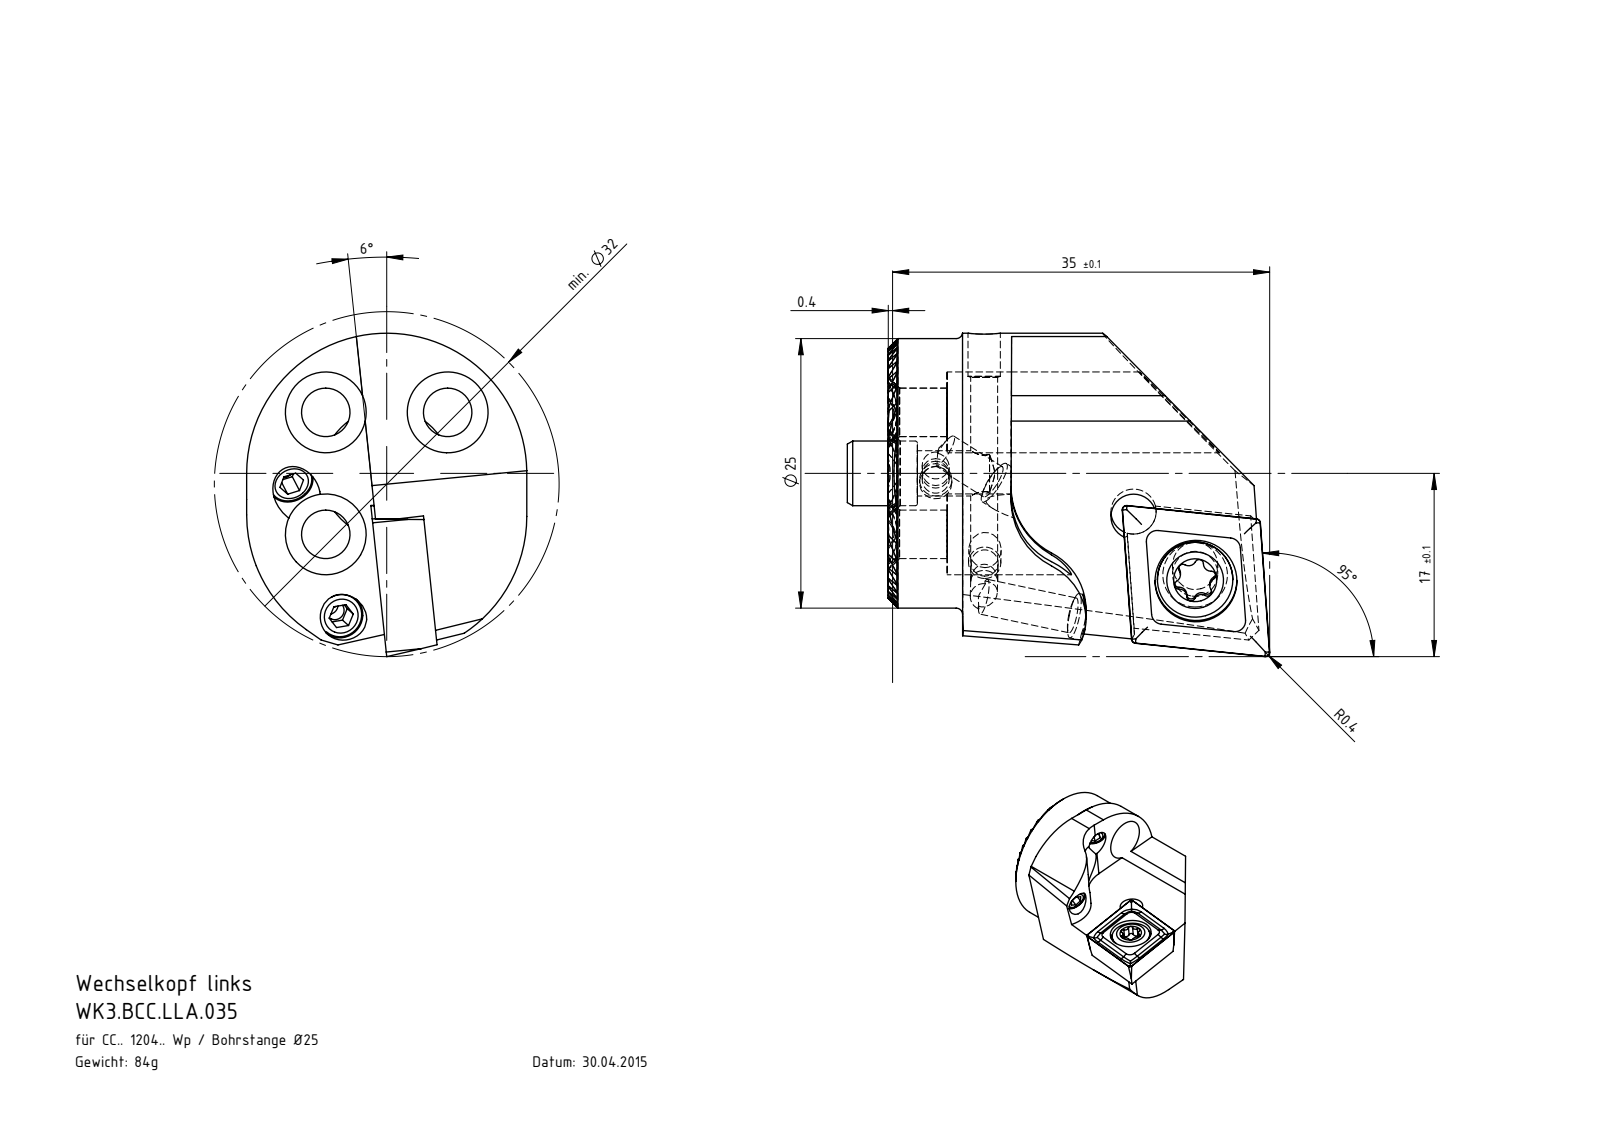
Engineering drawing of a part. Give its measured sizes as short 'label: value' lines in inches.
name: WK3.BCC.LLA.035; WK3-BCC.LLA.035_A; WCC-ER2.001.010_A; CCMT120404 (+3 more)
written by: SolidWorks 2017 (AUTOMOTIVE_DESIGN)
unit: in
bodies: 12 solids, 544 faces (186 planar, 179 cylindrical, 179 other)
size: 1.543 × 1.181 × 1.024
volume: 0.656 in³; area: 11.17 in²
holes: 5× ⌀0.165, 3× ⌀0.094, 3× ⌀0.098, 3× ⌀0.177, 3× ⌀0.295, 2× ⌀0.067, 2× ⌀0.118, 2× ⌀0.13, 1× ⌀0.217, 1× ⌀0.236, 1× ⌀0.299
bosses: 3× ⌀0.118, 2× ⌀0.157, 1× ⌀0.984, 1× ⌀0.472, 1× ⌀0.276, 1× ⌀0.197
rounds: 20× R0.005, 6× R0.015, 3× R0.027, 3× R0.027, 3× R0.512, 1× R0.236, 1× R0.276
face distances: 0.17, 0.043, 0.128, 0.213, 0.341, 0.176, 0.298, 0.085, 0.085, 0.383
hole spacings: 0.315, 0.446, 0.323, 0.328, 0.63
